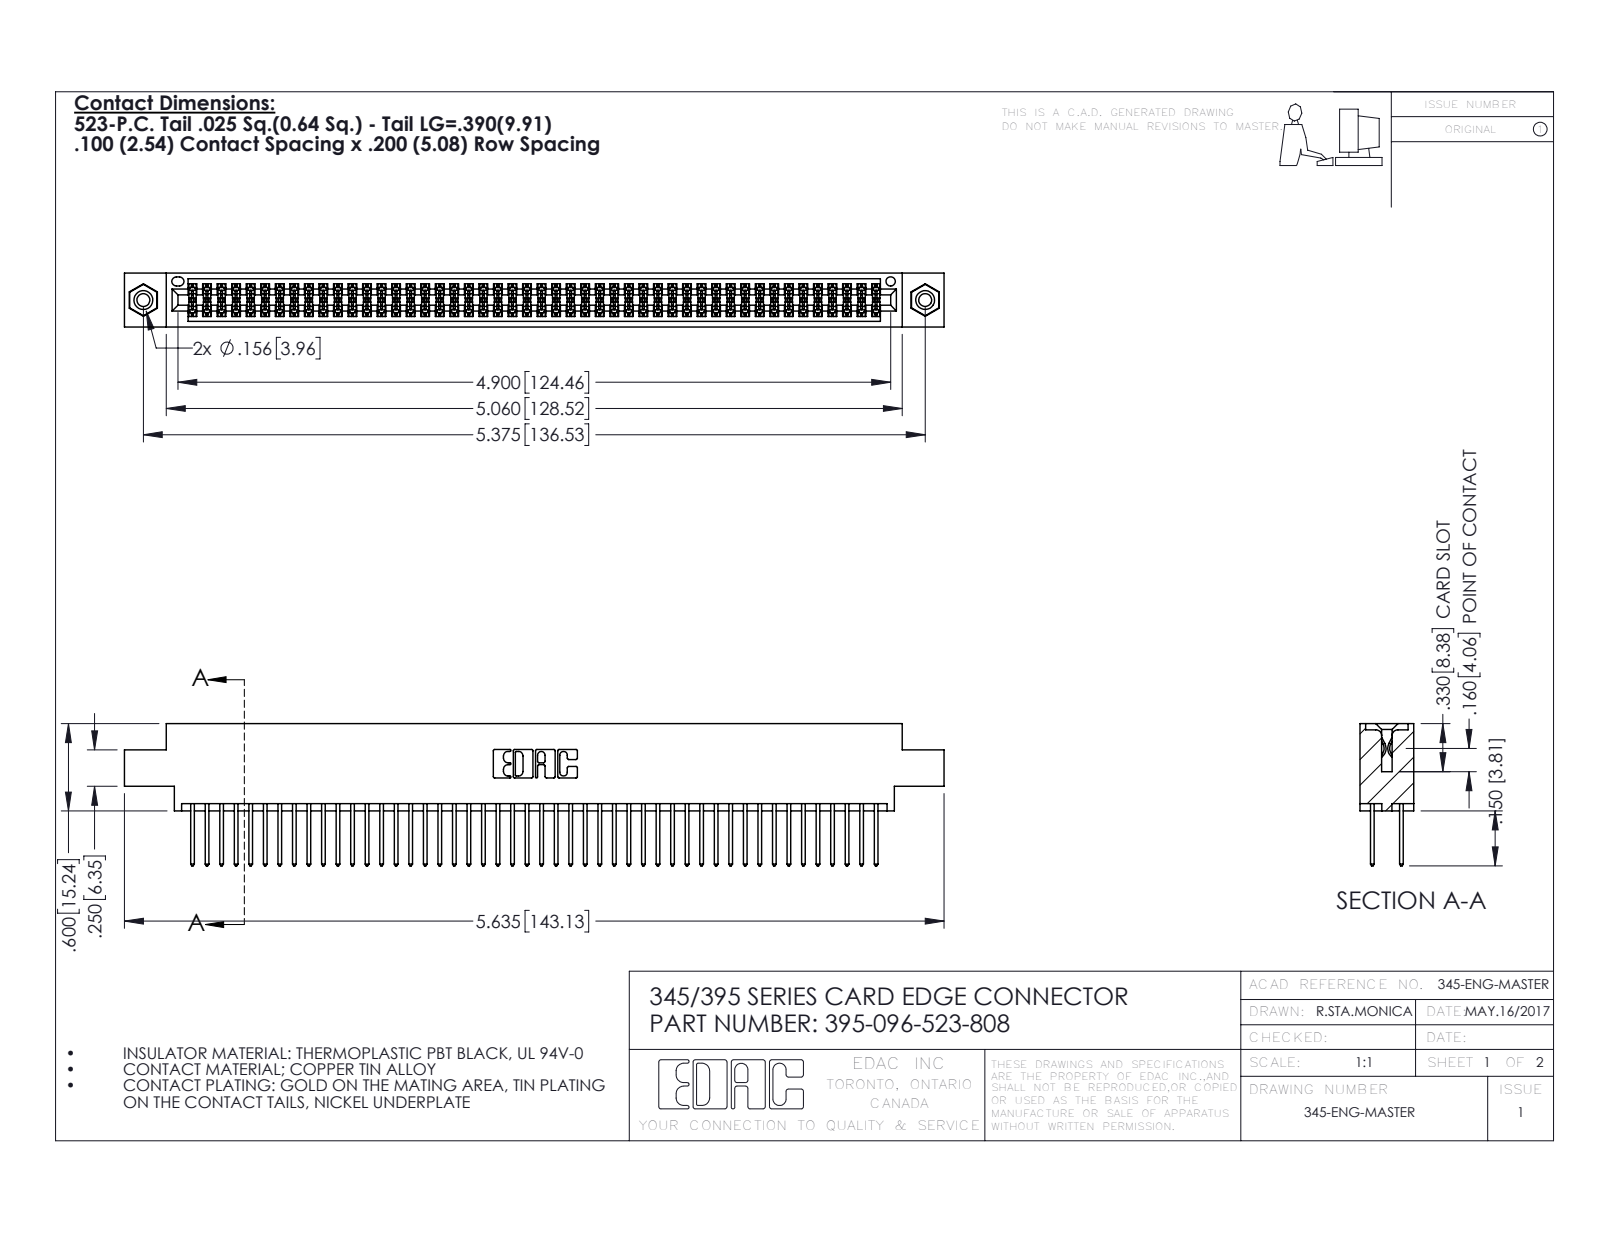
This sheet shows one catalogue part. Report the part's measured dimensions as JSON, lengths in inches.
{"part_name": "395-096-523-808; 345 Part_0.170 Offset - 0.156 Dia-TI; 345-250-001_345-250-003-102; 345-292-001_345-293-123", "step_written_by": "SolidWorks 2016 (CONFIG_CONTROL_DESIGN)", "units": "inches", "bodies": {"solids": 99, "faces": 4990, "planar": 3284, "cylindrical": 1690, "other": 16}, "overall_size": [5.635, 0.977, 0.37], "volume_in3": 0.857, "surface_area_in2": 33.95, "round_holes": [[0.089, 2], [0.125, 2], [0.156, 2], [0.064, 1]], "round_bosses_or_shafts": [[0.155, 2]], "partial_cylinders_radius": [[0.006, 144], [0.01, 96], [0.01, 22], [0.007, 6], [0.031, 6], [0.026, 3], [0.014, 2], [0.019, 2]], "face_to_face_distances": [0.072, 0.298, 0.2, 0.098, 0.272, 0.025, 0.37, 0.225, 0.175, 0.149], "hole_center_spacings": [0.27, 5.139, 5.375]}
